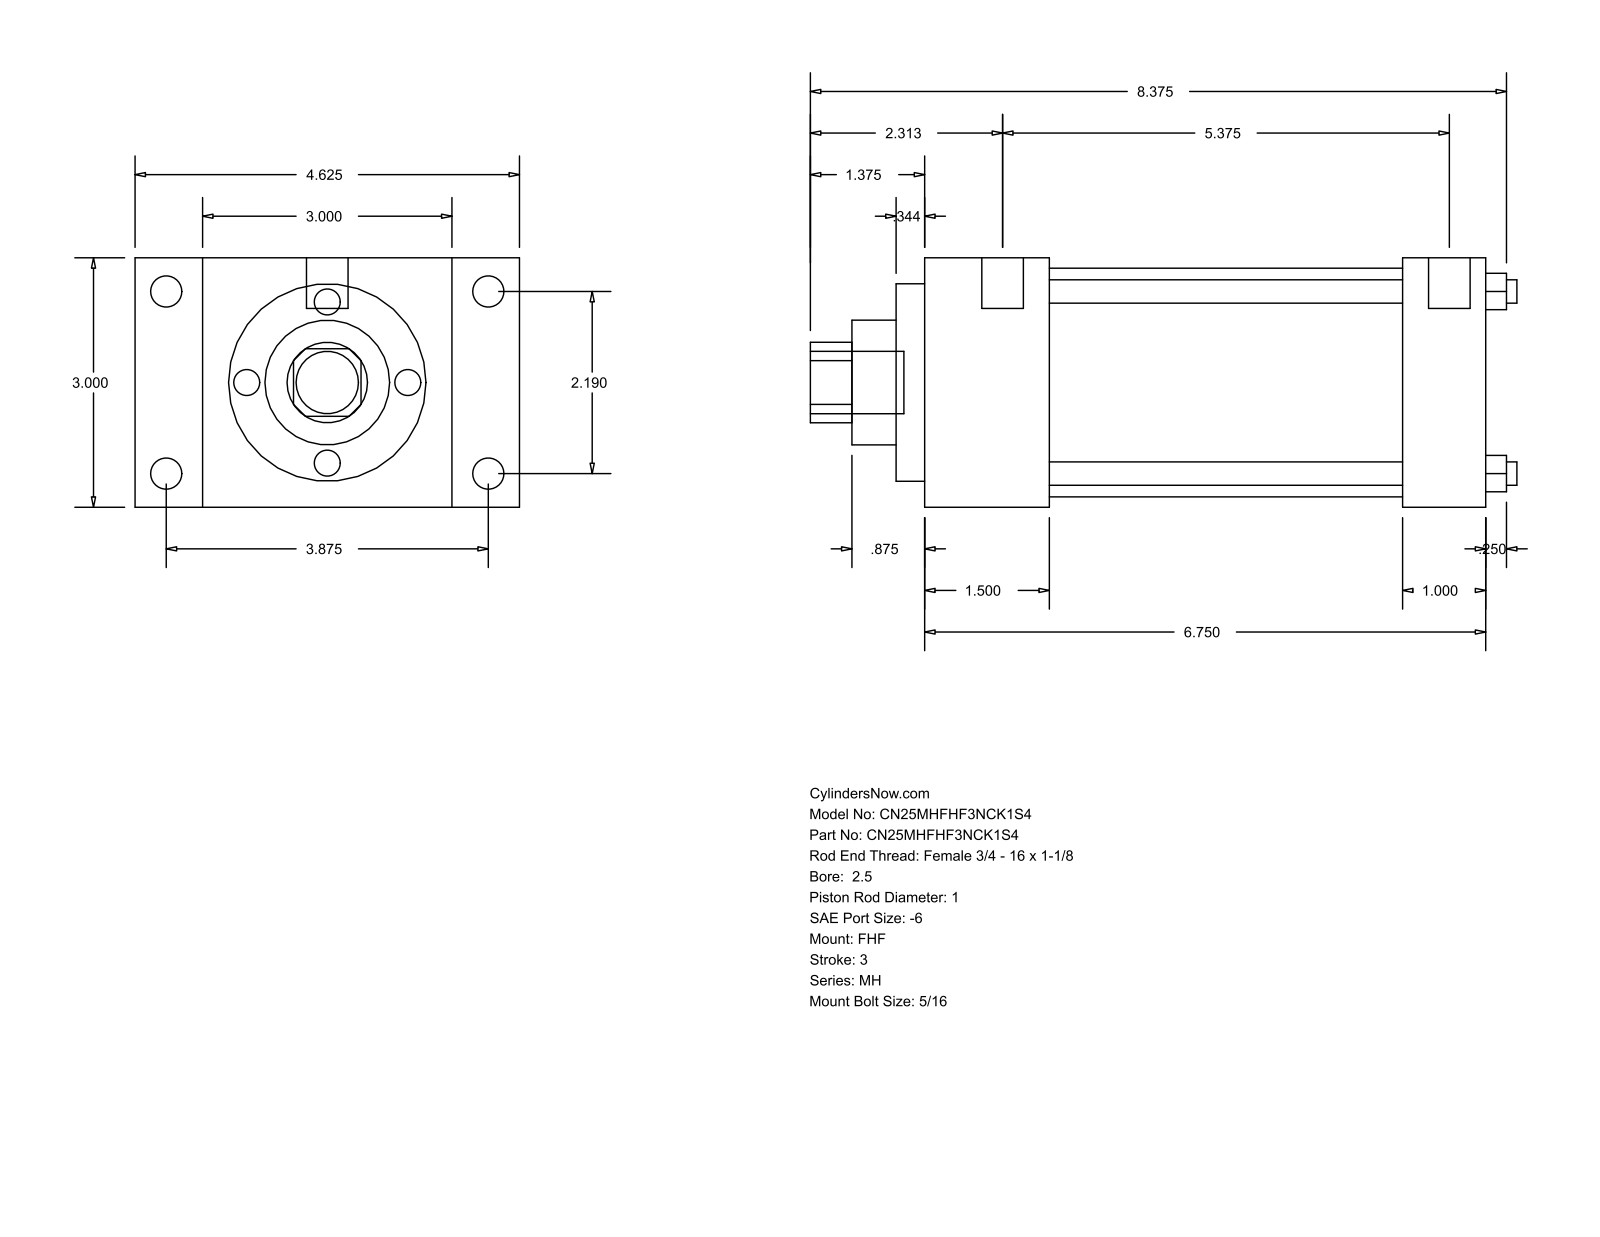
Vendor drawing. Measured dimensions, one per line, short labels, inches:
name: MH_FHF__0250_1
written by: GSSL Pune (CONFIG_CONTROL_DESIGN)
unit: in
bodies: 0 solids, 90 faces (61 planar, 29 cylindrical, 0 other)
size: 8.5 × 4.625 × 3
holes: 4× ⌀0.281, 1× ⌀1, 1× ⌀1.5, 1× ⌀2.375, 1× ⌀2.75
bosses: 4× ⌀0.375, 4× ⌀0.219, 2× ⌀0.5, 1× ⌀0.75
rounds: 1× R0.484
face distances: 3, 6.75, 1.5, 5.25, 0.813, 3.813, 4.625, 5.75, 4.25, 1
hole spacings: 1.548, 2.19, 3.097
